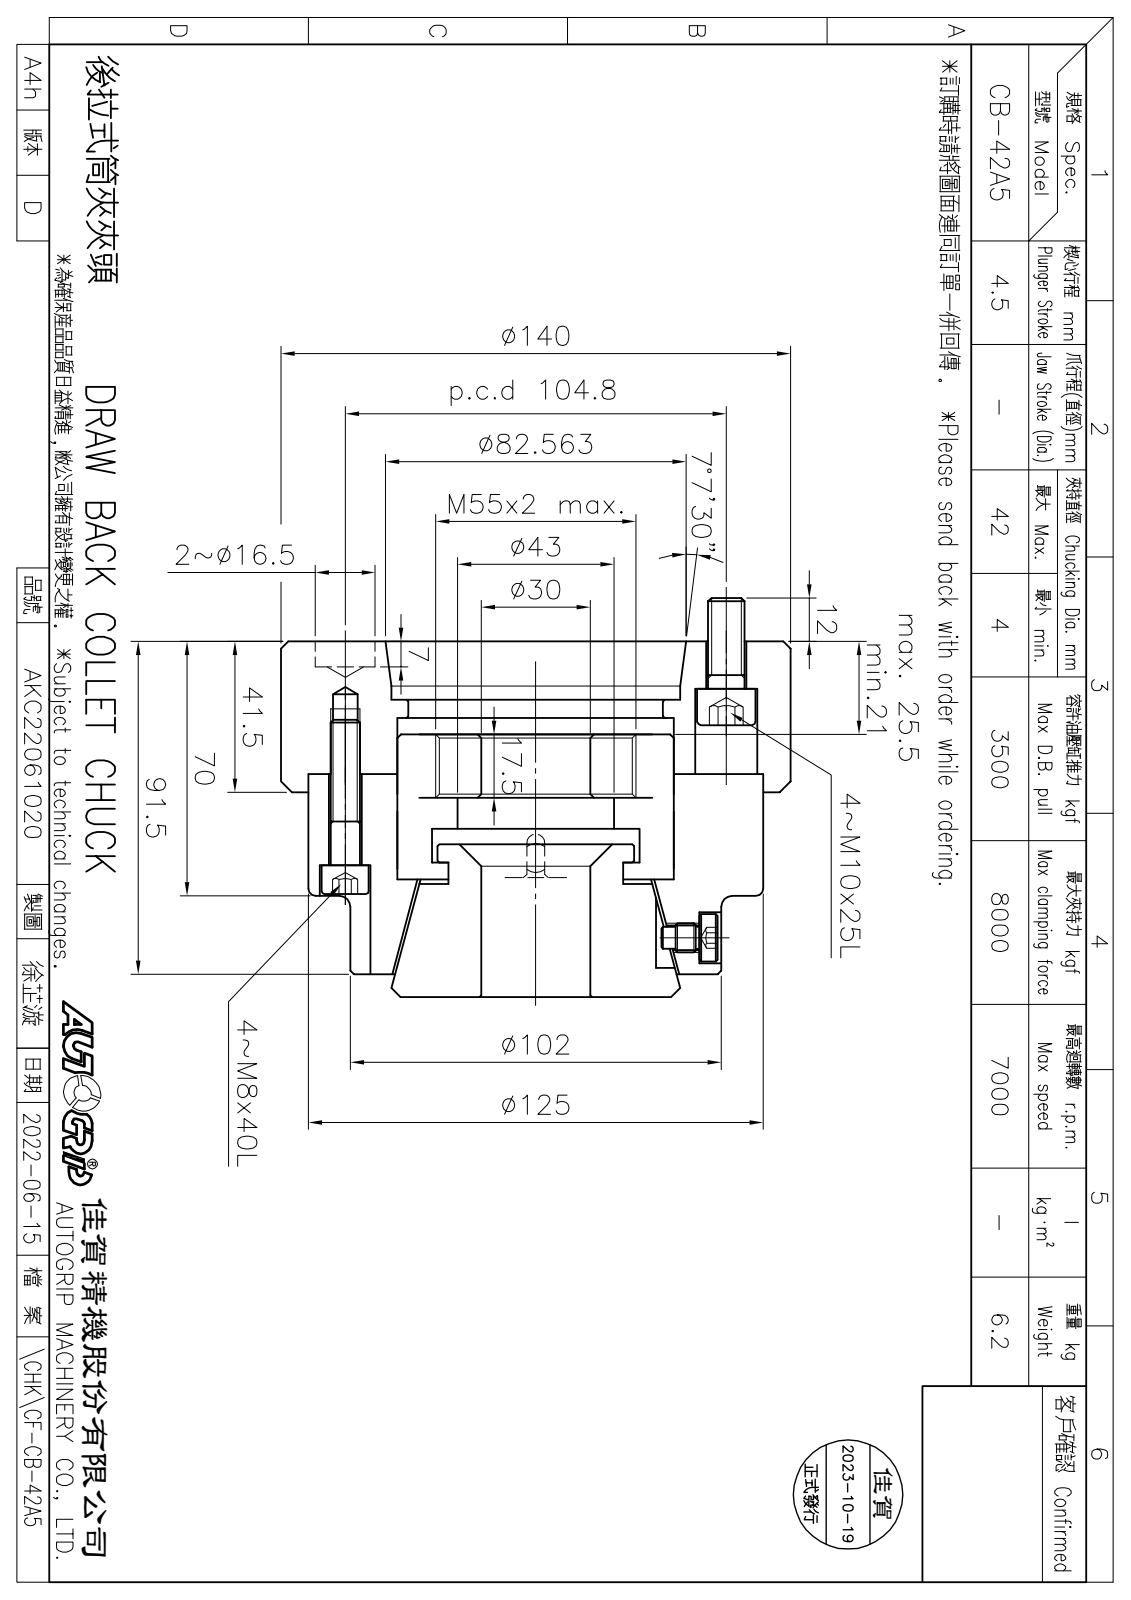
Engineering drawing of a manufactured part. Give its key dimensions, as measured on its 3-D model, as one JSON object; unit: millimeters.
{"part_name": "圓頭內六角螺栓_M8x40; CF-CB-42A5; CF-CB-42-02010; CF-RG-42R_RG42RM60 (+3 more)", "step_written_by": "SolidWorks 2020 (CONFIG_CONTROL_DESIGN)", "units": "millimeters", "bodies": {"solids": 12, "faces": 395, "planar": 148, "cylindrical": 127, "other": 120}, "overall_size": [140, 140, 109.7], "volume_mm3": 941104, "surface_area_mm2": 171733, "round_holes": [[5, 4], [6.8, 4], [9, 4], [11, 4], [14, 4], [17, 4], [8.5, 3], [16.5, 2], [29.7, 1], [43, 1], [50, 1], [53, 1]], "round_bosses_or_shafts": [[16, 4], [13, 4], [10, 4], [8, 4], [140, 1], [102, 1], [54, 1], [48.5, 1]], "face_to_face_distances": [36.5, 65.5, 29, 26, 97.7, 61.2, 32.2, 16, 25.5, 28.5], "hole_center_spacings": [52.4, 37.89, 40.1, 69.07, 74.1, 90.03, 96.82, 7.4]}
